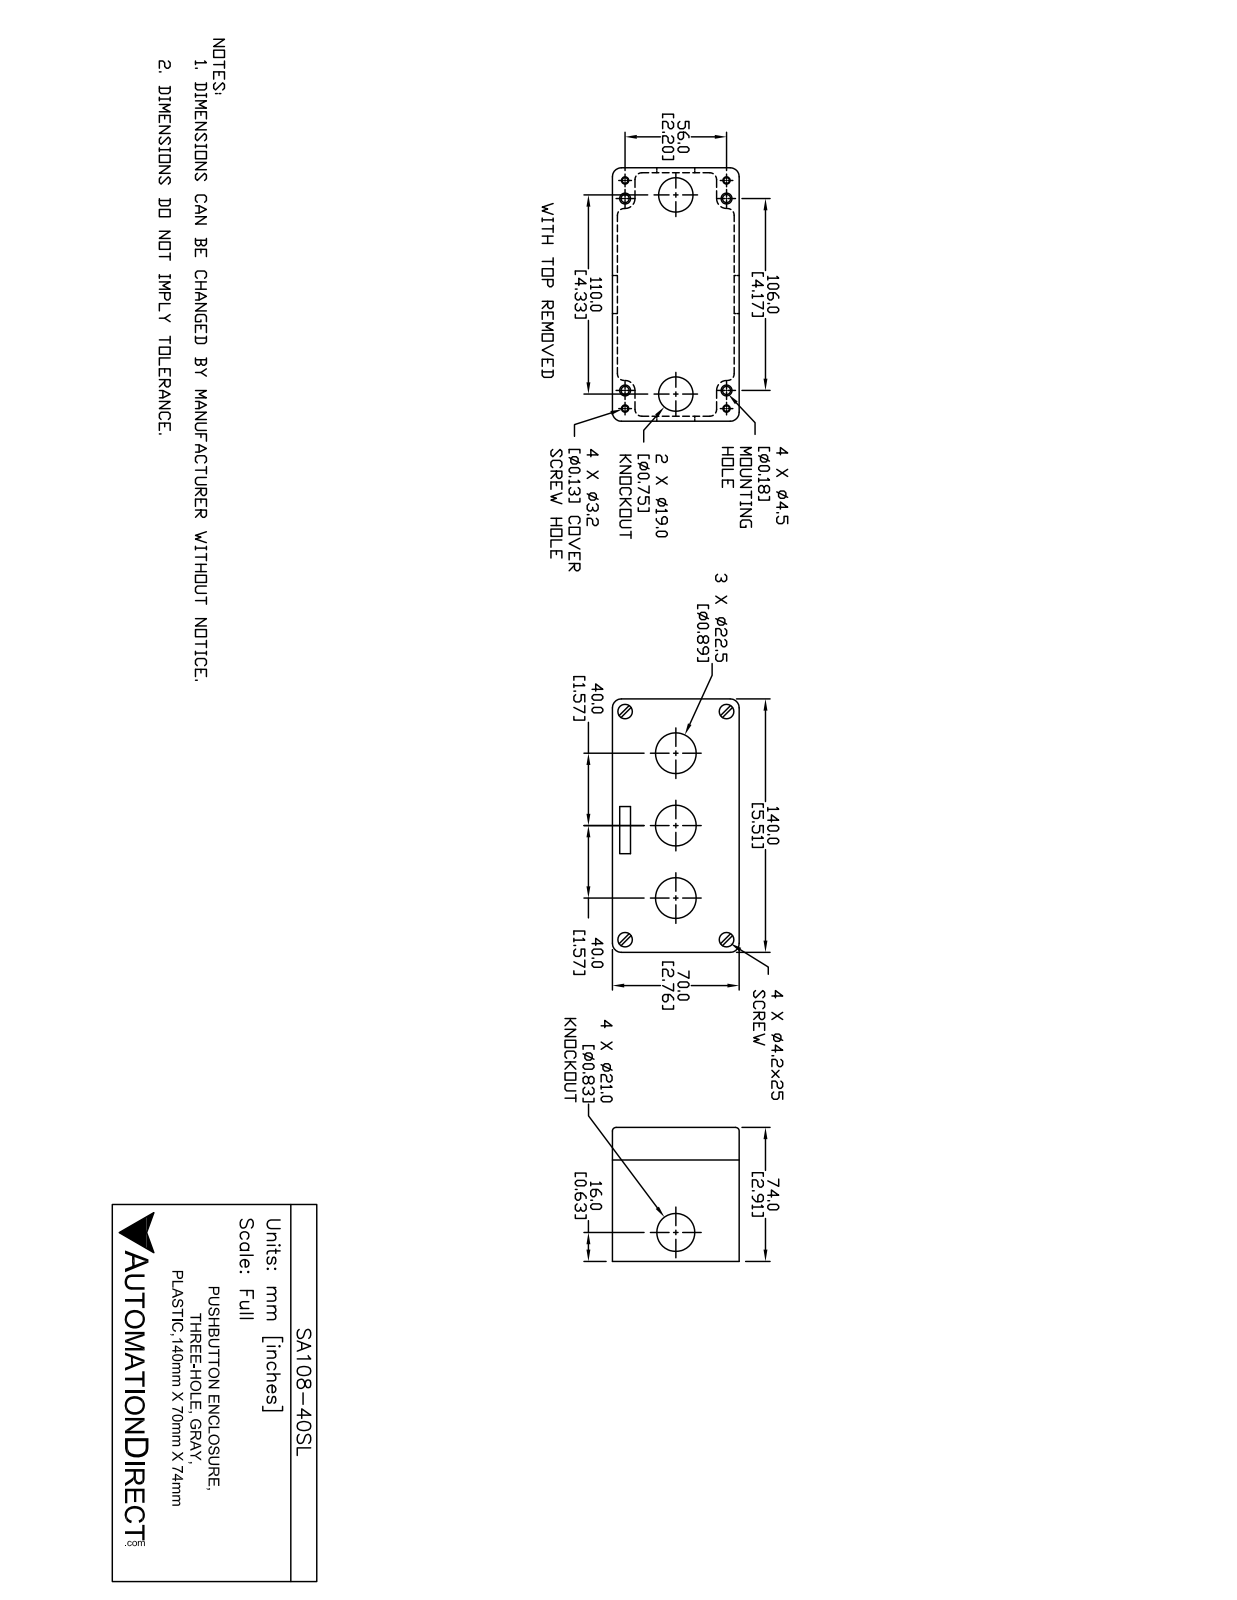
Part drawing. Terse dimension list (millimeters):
name: SA108-40SL
written by: SolidWorks 2018 (AUTOMOTIVE_DESIGN)
unit: mm
bodies: 6 solids, 475 faces (127 planar, 194 cylindrical, 154 other)
size: 140 × 74.2 × 70
volume: 177 300 mm³; area: 102 700 mm²
holes: 4× ⌀3.2, 4× ⌀4.2, 4× ⌀4.5, 4× ⌀7.5, 4× ⌀8, 3× ⌀22.5, 2× ⌀19, 2× ⌀21
bosses: 4× ⌀7.4, 4× ⌀2.8
rounds: 16× R0.5, 8× R1, 8× R2.4, 4× R1, 4× R1.8, 4× R5, 4× R6.6, 4× R8.2
face distances: 2.6, 67.4, 70, 2.2, 74, 71.9, 64.8, 2, 72.1, 69.9
hole spacings: 10, 28.1, 29.1, 30.9, 36.2, 56, 56.9, 59.9
